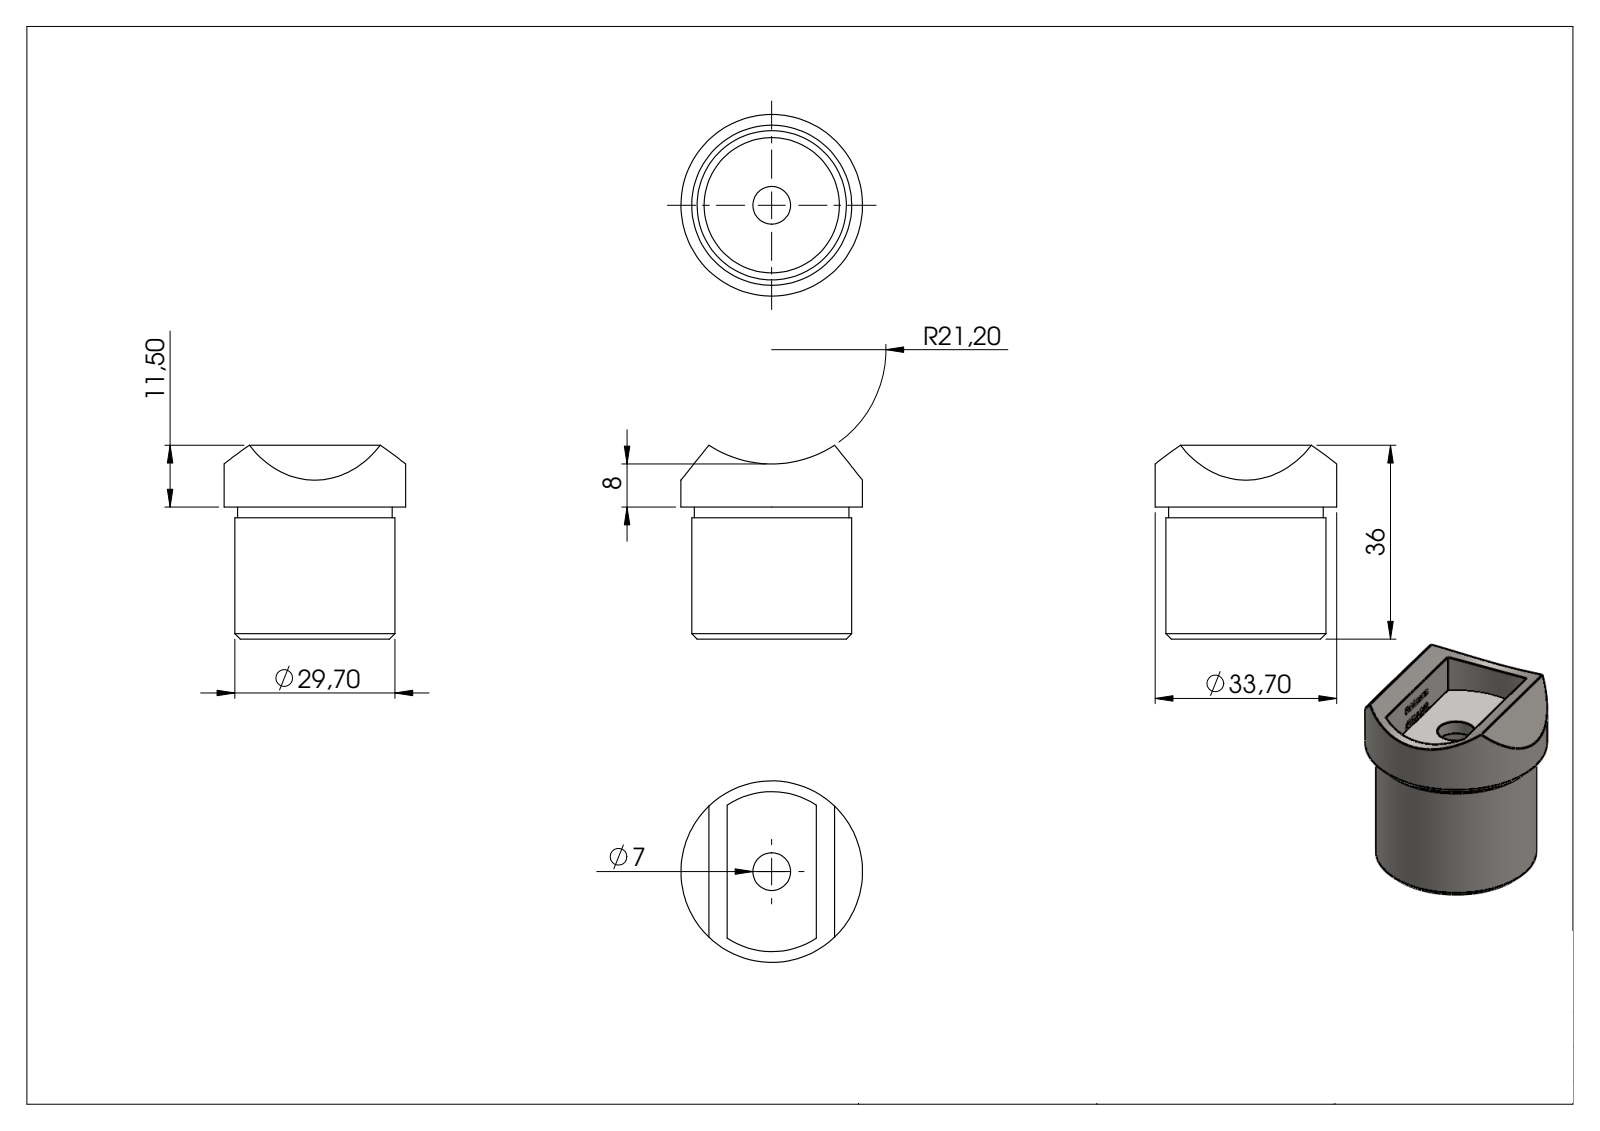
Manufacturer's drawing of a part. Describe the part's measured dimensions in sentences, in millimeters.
The part is named "60214-240". Its 3-D file was written by "SolidWorks 2015 (CONFIG_CONTROL_DESIGN)". It is 1 solid with 241 faces: 139 planar, 13 cylindrical and 89 other. Overall it measures 36 by 33.7 by 33.7 millimeters. Its volume is 9 842 cubic millimeters and its surface area 7 586 square millimeters. Round holes: 1 of diameter 7, 1 of diameter 25.1, 1 of diameter 29.7. Round bosses or shafts: 1 of diameter 33.7, 1 of diameter 28.7. Partial cylindrical surfaces (rounded edges, fillets, slot ends): 1 of radius 21.2. The main face-to-face distances are 2.5, 16.56, 24.5, 27, 4.5, 22.5, 2, 16.66, 0.39, 2.89.
